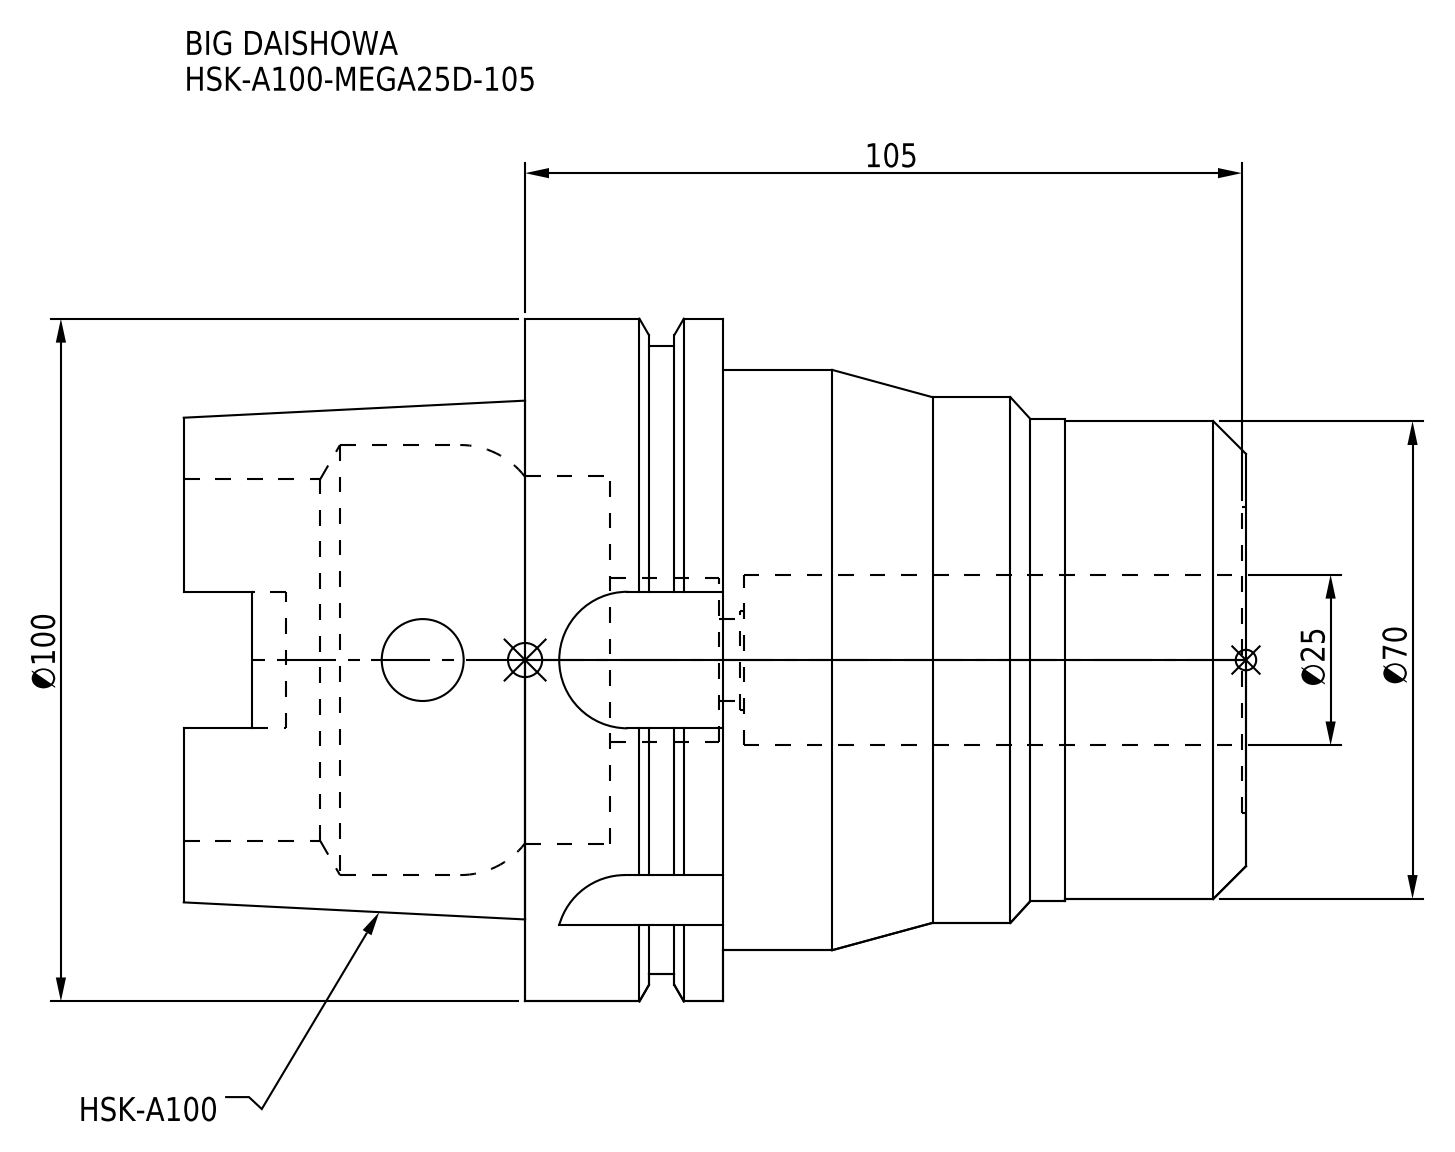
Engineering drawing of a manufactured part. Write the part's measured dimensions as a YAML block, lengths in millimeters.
part_name: "HSK-A100-MEGA25D-105"
step_written_by: "CREO PARAMETRIC BY PTC INC, 2016380 (AUTOMOTIVE_DESIGN)"
units: millimeters
bodies: {solids: 1, faces: 102, planar: 36, cylindrical: 46, other: 20}
overall_size: [155.6, 100, 100]
volume: 567989
surface_area: 72188
round_holes:
  - {diameter: 12, count: 2}
  - {diameter: 14.5, count: 1}
  - {diameter: 24, count: 1}
  - {diameter: 25, count: 1}
  - {diameter: 44.8, count: 1}
  - {diameter: 53, count: 1}
  - {diameter: 53.8, count: 1}
  - {diameter: 63, count: 1}
round_bosses_or_shafts:
  - {diameter: 100, count: 1}
  - {diameter: 92, count: 1}
  - {diameter: 85, count: 1}
  - {diameter: 77, count: 1}
  - {diameter: 70.7, count: 1}
  - {diameter: 70, count: 1}
partial_cylinders:
  - {radius: 4.88, count: 4}
  - {radius: 10, count: 4}
face_to_face_distances: [29, 16.55, 12.45, 76.6, 93.15, 105.6, 0.6, 76, 92.55, 105]
